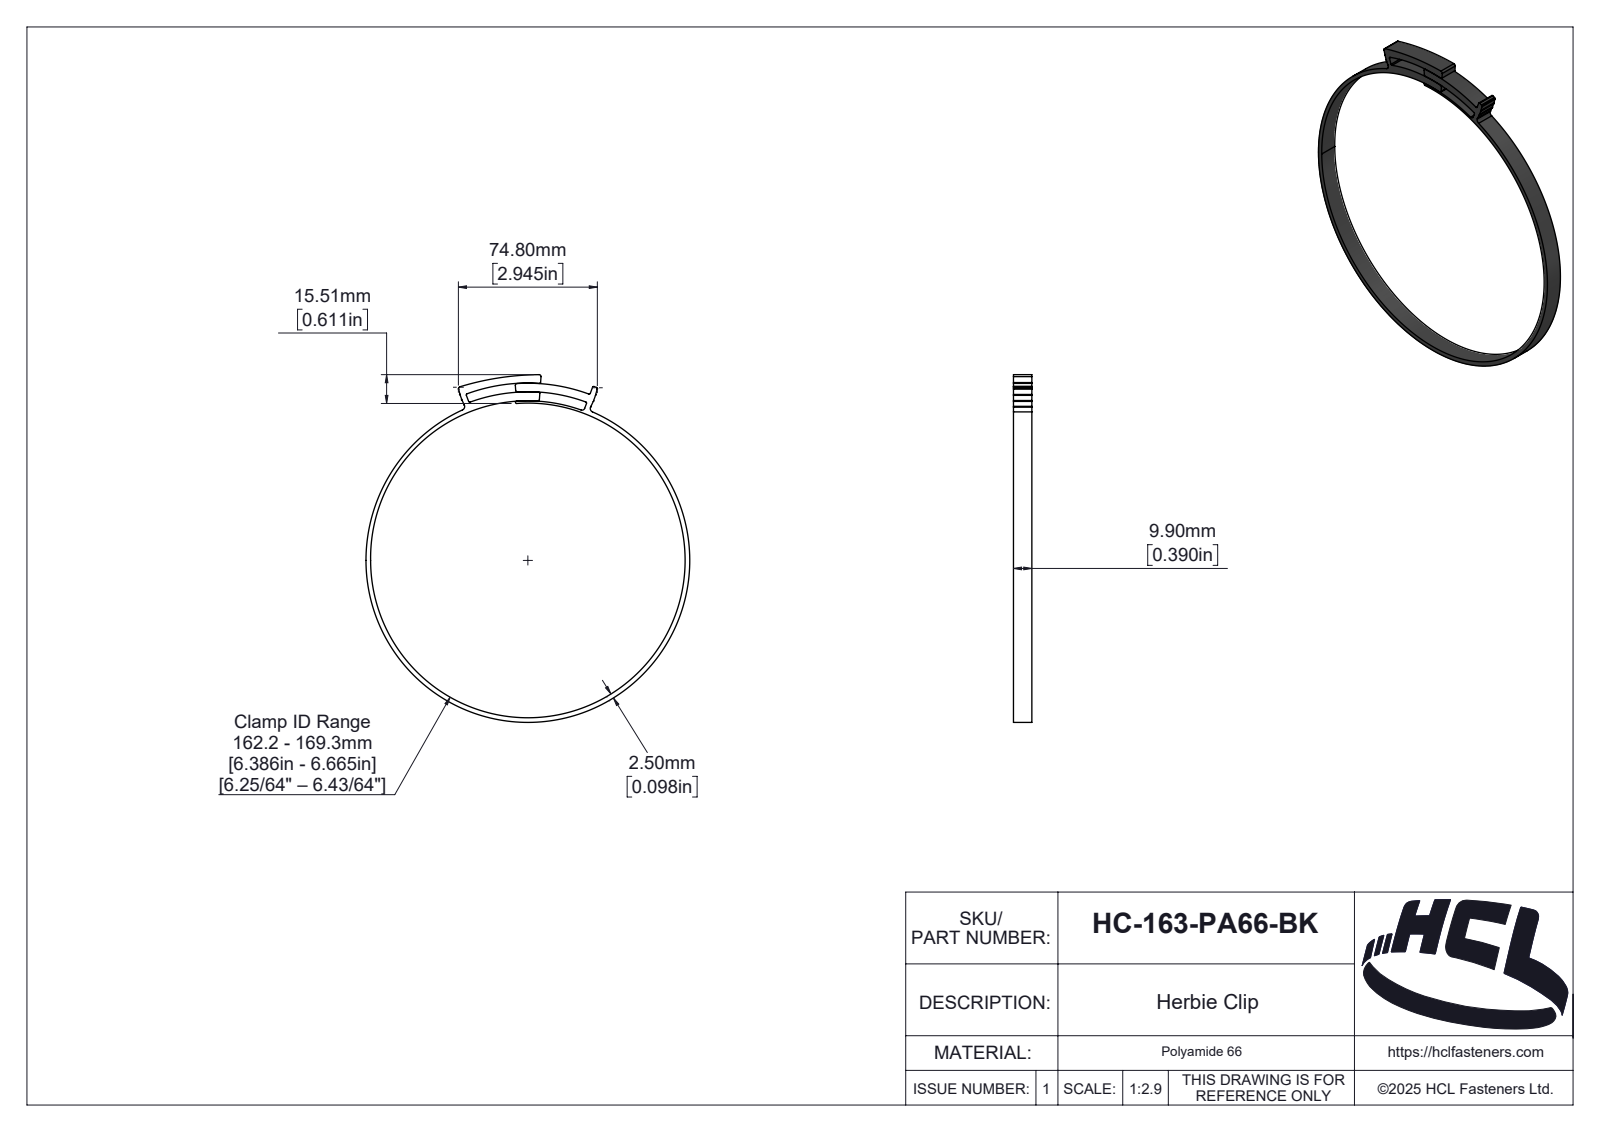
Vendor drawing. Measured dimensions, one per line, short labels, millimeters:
name: HC-163-PA66-BK
written by: SolidWorks 2025 (AUTOMOTIVE_DESIGN)
unit: mm
bodies: 1 solid, 161 faces (13 planar, 99 cylindrical, 49 other)
size: 187.1 × 174.3 × 9.9
volume: 18 109 mm³; area: 16 745 mm²
rounds: 8× R0.25, 7× R0.6, 5× R1, 2× R2, 1× R0.17, 1× R0.67, 1× R0.84, 1× R0.89
face distances: 9.9
